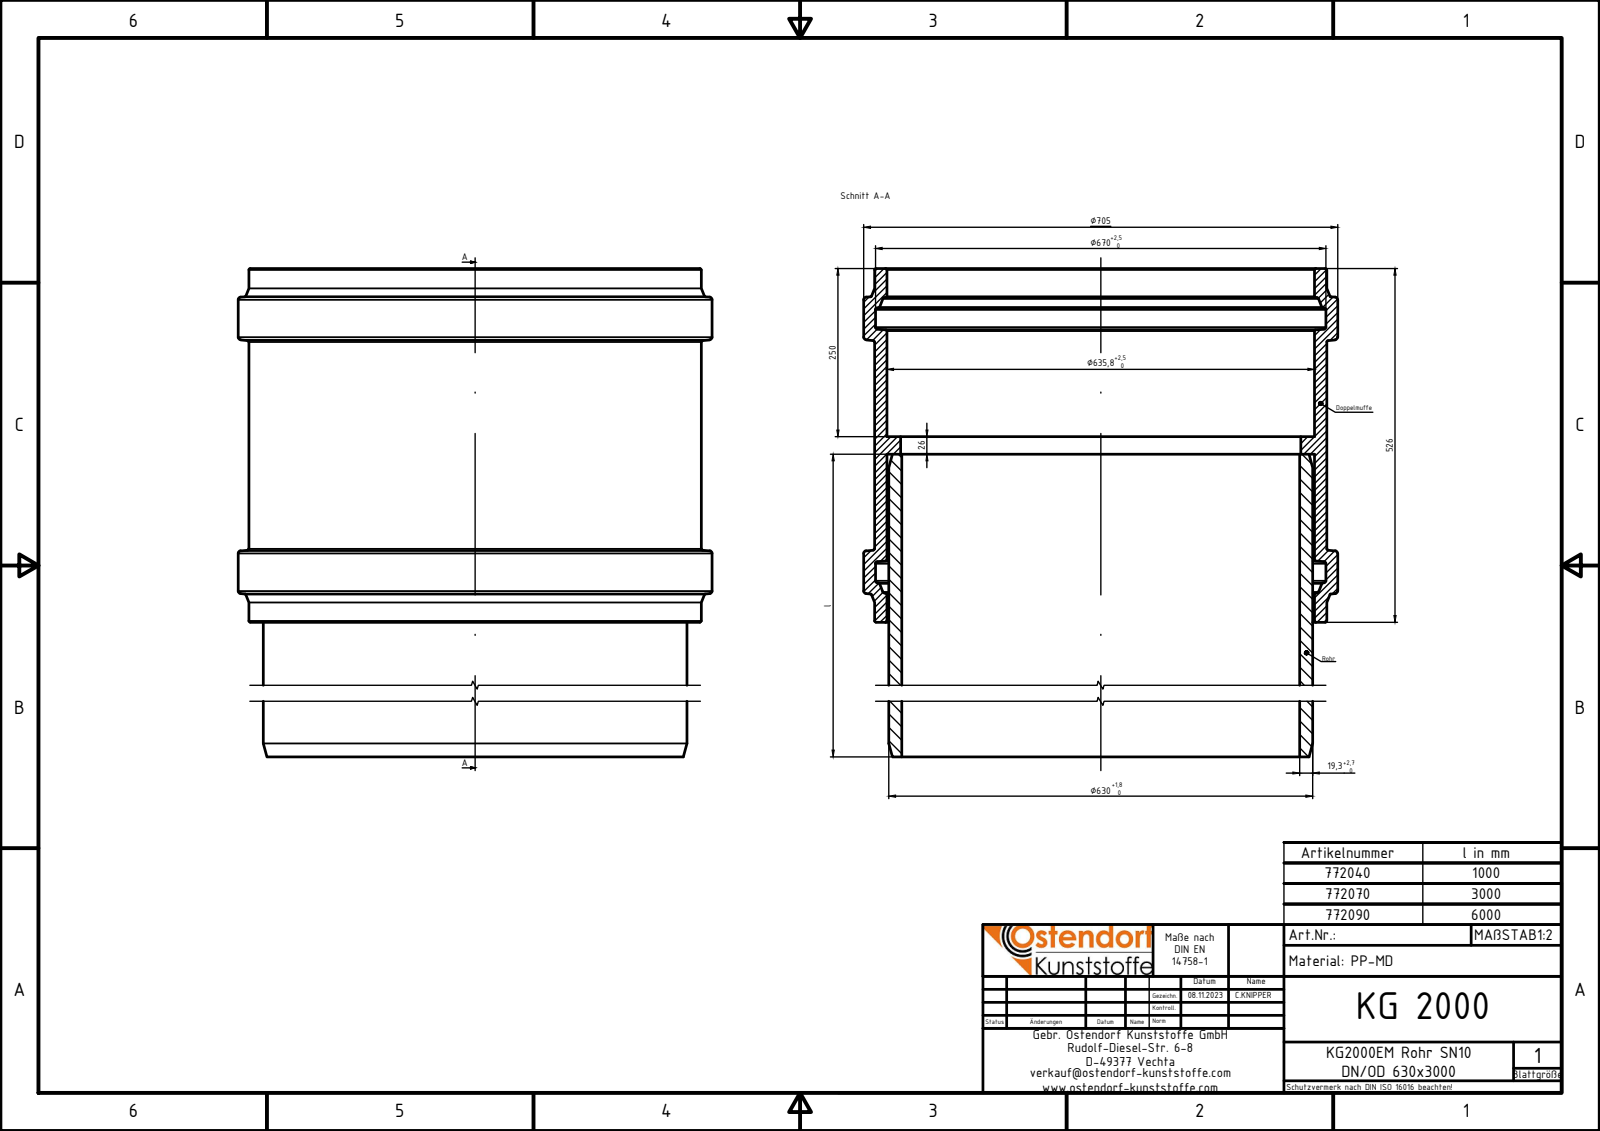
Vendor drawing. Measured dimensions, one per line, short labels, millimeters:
name: 772070z
written by: Autodesk Inventor 2024 (AUTOMOTIVE_DESIGN)
unit: mm
bodies: 1 solid, 60 faces (6 planar, 14 cylindrical, 40 other)
size: 3276 × 704.8 × 704.8
volume: 133 600 000 mm³; area: 14 040 000 mm²
holes: 1× ⌀591.4, 1× ⌀594.8, 1× ⌀635.8, 1× ⌀670
bosses: 1× ⌀704.8, 1× ⌀672.6, 1× ⌀630
face distances: 276, 250, 526, 2750, 3026, 3276, 3000, 26
